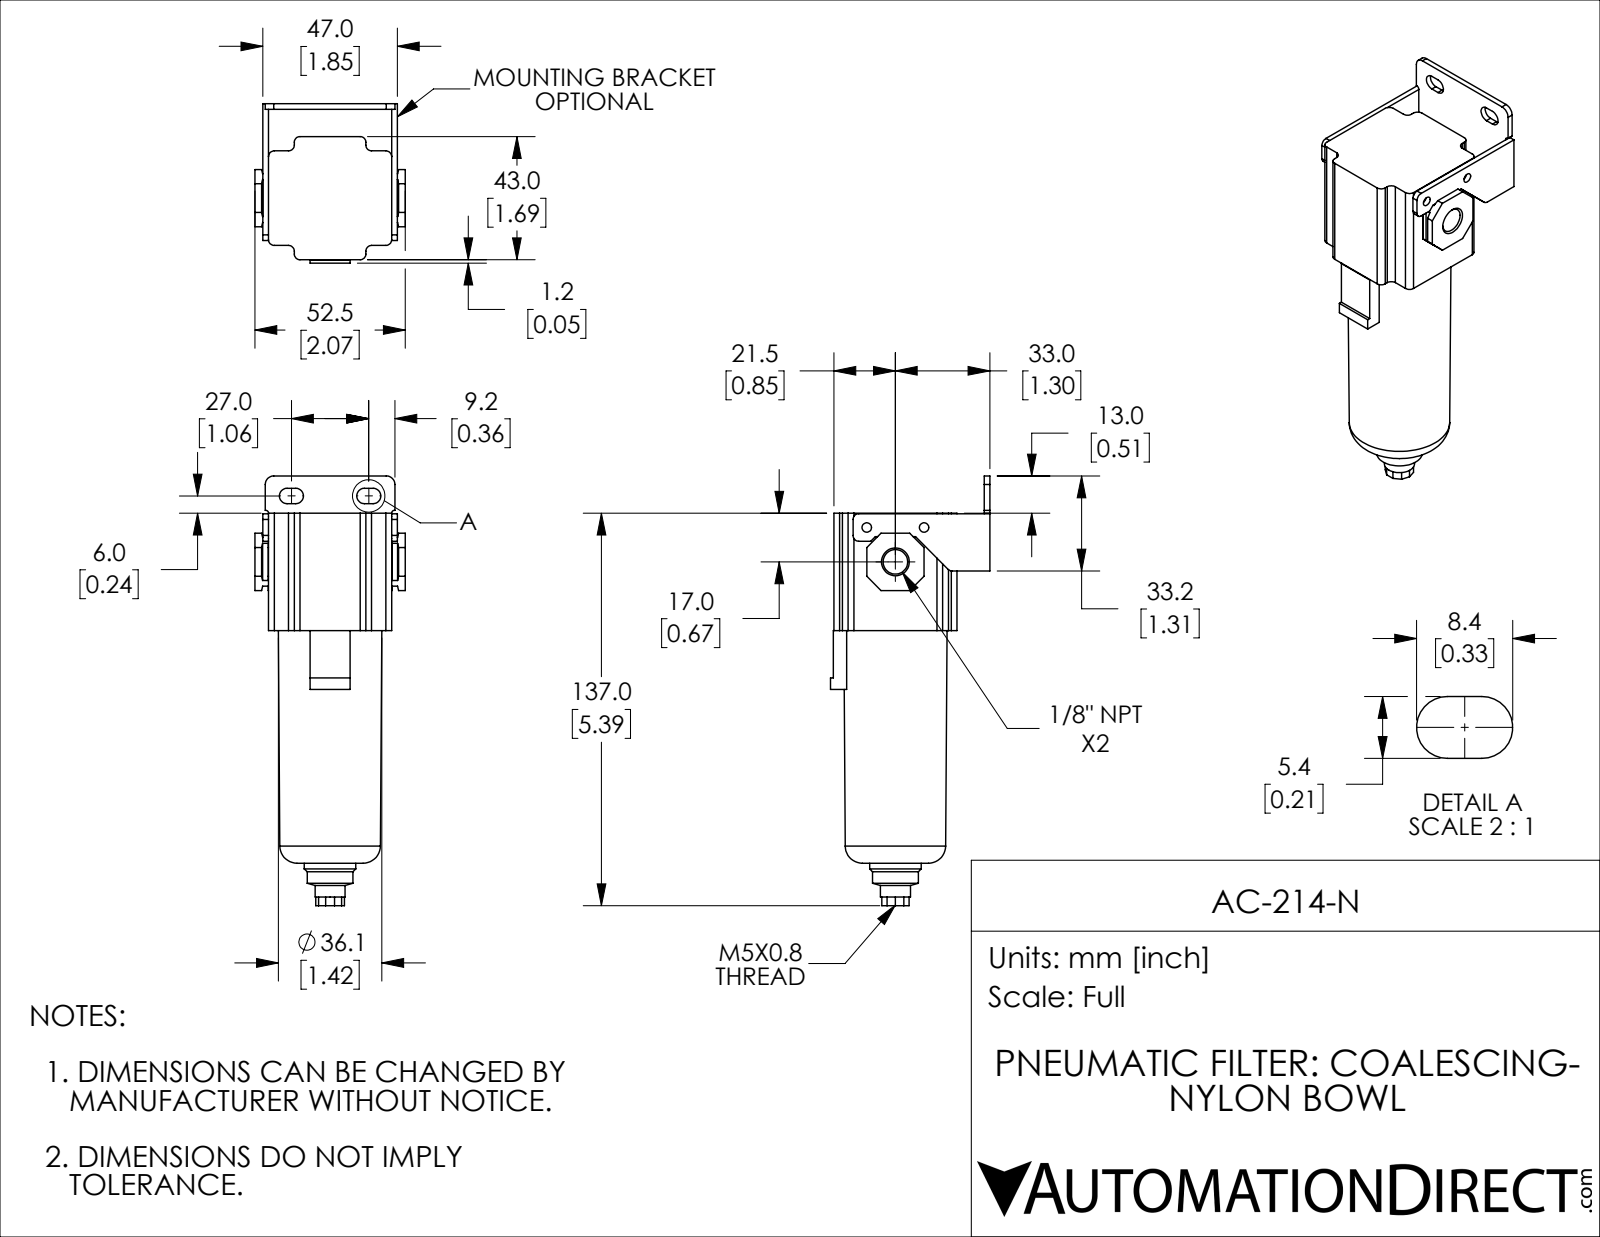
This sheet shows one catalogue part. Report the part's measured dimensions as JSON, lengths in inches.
{"part_name": "AC-214-N", "step_written_by": "SolidWorks 2018 (AUTOMOTIVE_DESIGN)", "units": "inches", "bodies": {"solids": 1, "faces": 187, "planar": 125, "cylindrical": 48, "other": 14}, "overall_size": [5.906, 2.192, 2.067], "volume_in3": 9.675, "surface_area_in2": 40.37, "round_holes": [[0.13, 2], [0.163, 1], [0.337, 1]], "round_bosses_or_shafts": [[0.709, 1], [0.63, 1], [0.413, 1]], "partial_cylinders_radius": [[0.079, 15], [0.106, 4], [0.039, 2], [0.118, 2]], "face_to_face_distances": [0.079, 1.693, 1.772, 2.067, 0.453, 2.146, 0.374, 0.197, 1.496, 1.614], "hole_center_spacings": [0.615, 0.787]}
